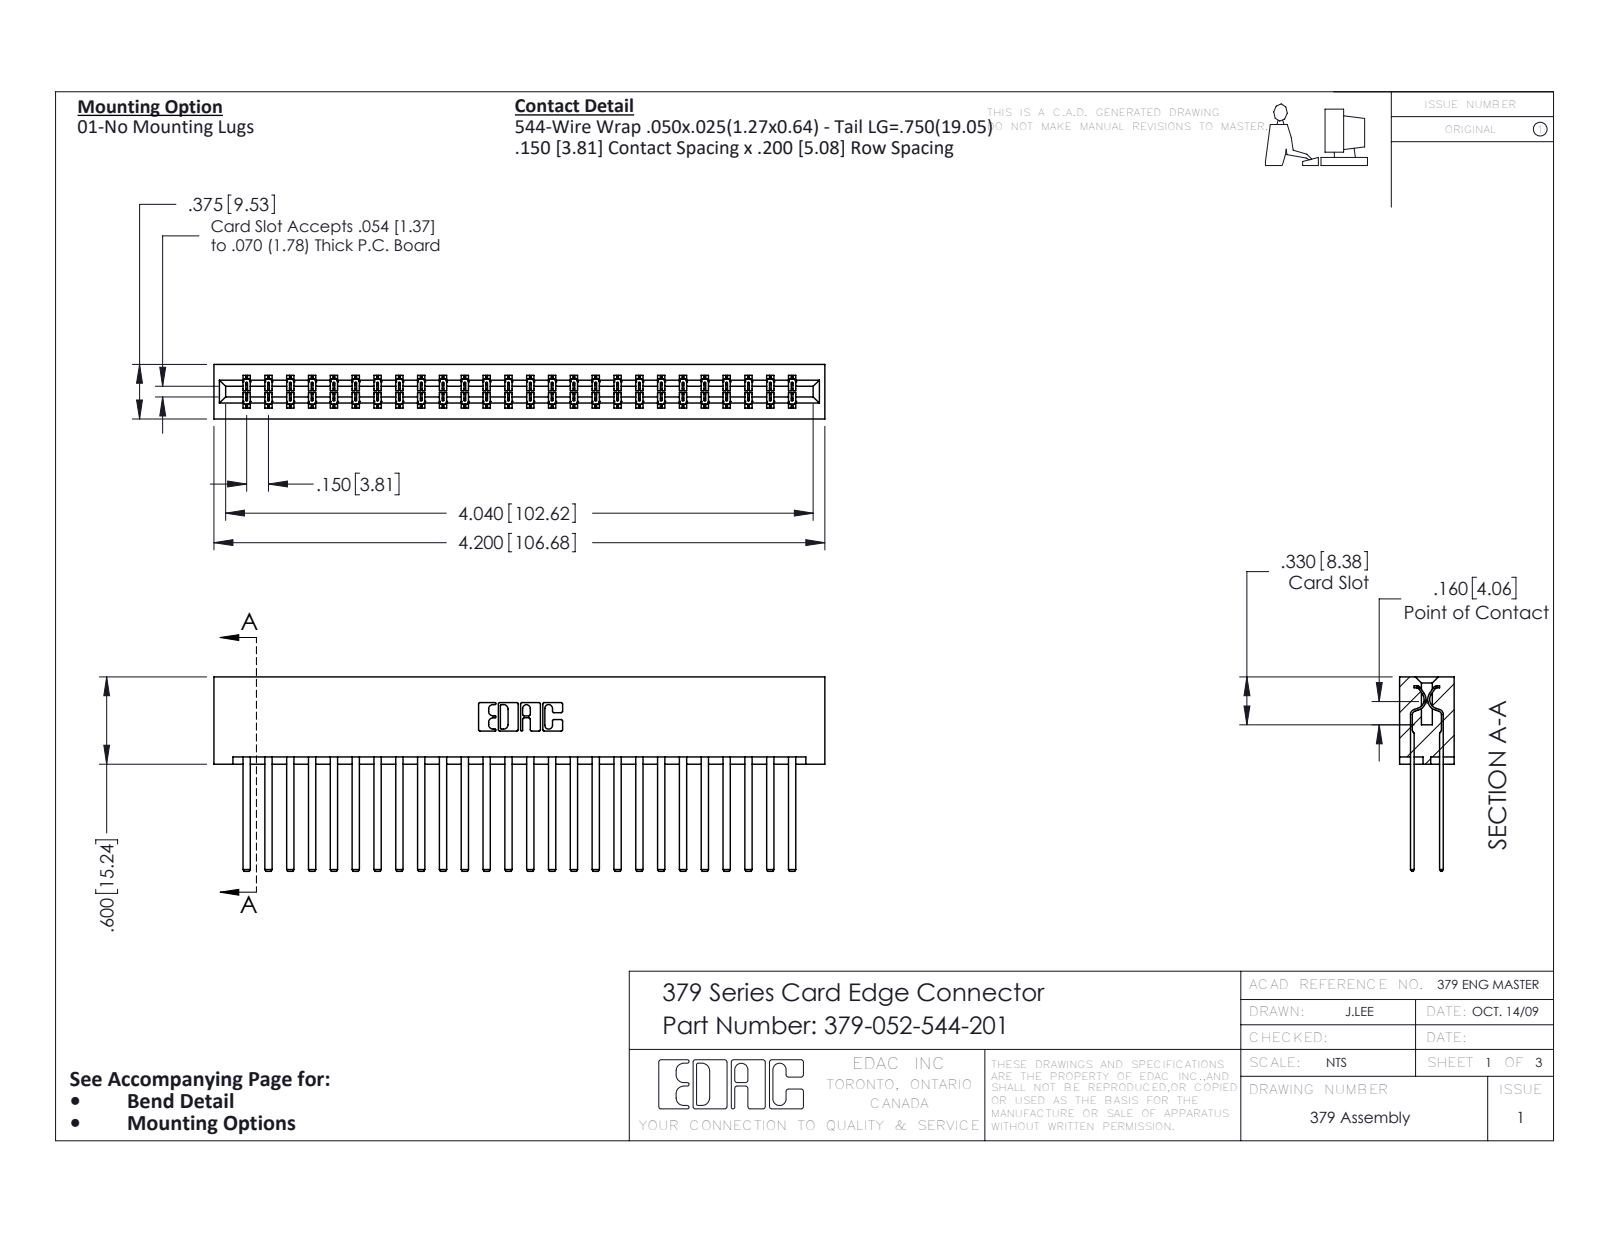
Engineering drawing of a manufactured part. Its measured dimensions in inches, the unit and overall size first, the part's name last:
Units: inches
Overall size (bounding box): 4.2 × 1.337 × 0.375
Partial cylindrical surfaces — rounded edges, fillets, slot ends (radius × count): R0.006 ×78, R0.01 ×22, R0.007 ×6, R0.031 ×6, R0.026 ×3, R0.014 ×2, R0.022 ×2, R0.024 ×2
Main face-to-face distances: 0.3, 0.1, 0.075, 0.2, 0.275, 0.375, 0.025, 0.15, 0.076, 0.15
Volume: 0.771 in³ · Surface area: 25.53 in²
Bodies: 53 solids, 2498 faces (1730 planar, 768 cylindrical, 0 other)
Part name (STEP PRODUCT): 379-052-544-201; 379 Part_Lugless; 345-292-001_345-293-144
STEP written by: SolidWorks 2016 (CONFIG_CONTROL_DESIGN)
